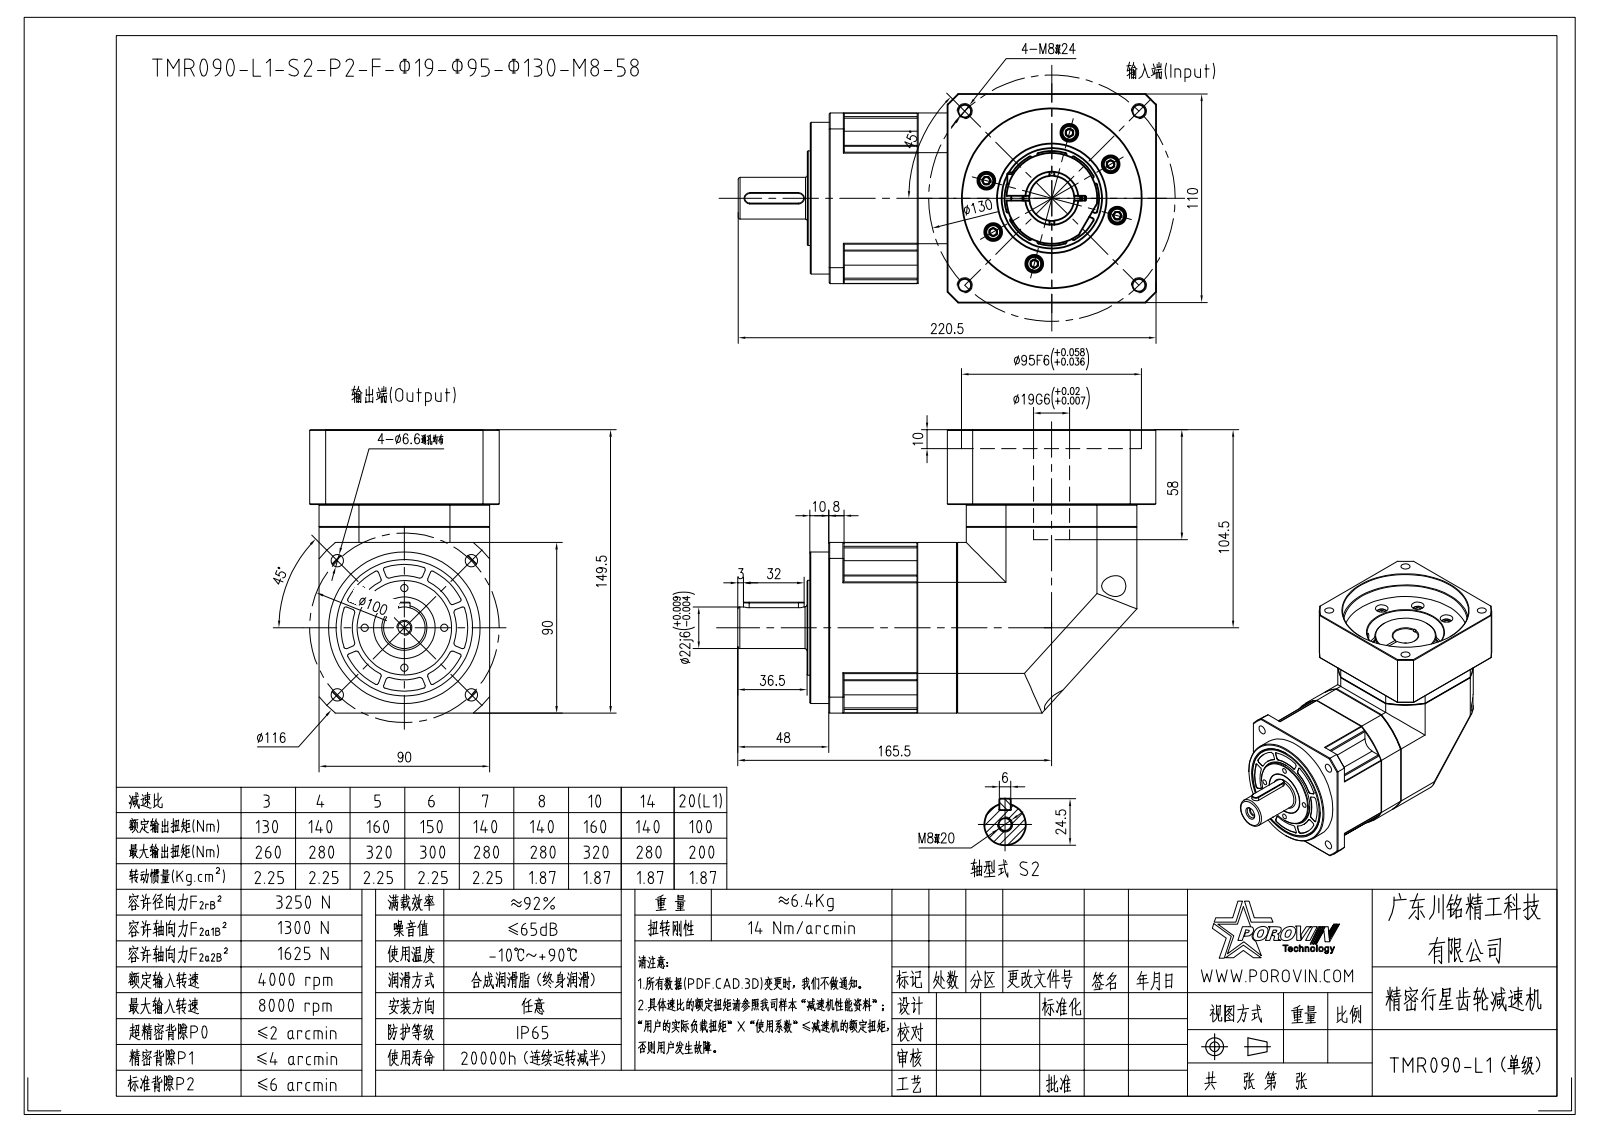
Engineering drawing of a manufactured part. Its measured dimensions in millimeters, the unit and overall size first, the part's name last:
Units: millimetres
Overall size (bounding box): 220.48 × 149.5 × 109.96
Round holes (diameter × count): ⌀5.4 ×12, ⌀5.5 ×12, ⌀9.5 ×12, ⌀4.2 ×7, ⌀5 ×5, ⌀6.5 ×5, ⌀6.8 ×5, ⌀4 ×4, ⌀6.6 ×4, ⌀6.68 ×4, ⌀11 ×4, ⌀8.4 ×1
Round bosses / shafts (diameter × count): ⌀8.5 ×12, ⌀8 ×12, ⌀5 ×12, ⌀10 ×4, ⌀9.88 ×4, ⌀6 ×4, ⌀80 ×1, ⌀78 ×1
Partial cylindrical surfaces — rounded edges, fillets, slot ends (radius × count): R1 ×92, R7.5 ×4, R51 ×3, R3 ×2, R4 ×1, R5.25 ×1, R40 ×1, R49.24 ×1
Main face-to-face distances: 90, 12, 9.98, 99.98, 51.5, 21.3, 21.5, 20, 31.5, 39.5
Hole centre spacings: 35.75, 27.36, 38.16, 66.06, 66.53, 86.78, 31.84, 75.16
Volume: 1 490 000 mm³ · Surface area: 231 220 mm²
Bodies: 42 solids, 1278 faces (514 planar, 551 cylindrical, 213 other)
Part name (STEP PRODUCT): HEXAGON_SOCKET_HEAD_CAP_S-15030; HEXAGON_SOCKET_HEAD_CAP_SC-4404; TMR900004_1; SPRING_LOCK_WASHERS--NORM-14923 (+8 more)
STEP written by: CREO PARAMETRIC BY PTC INC, 2020053 (CONFIG_CONTROL_DESIGN)
